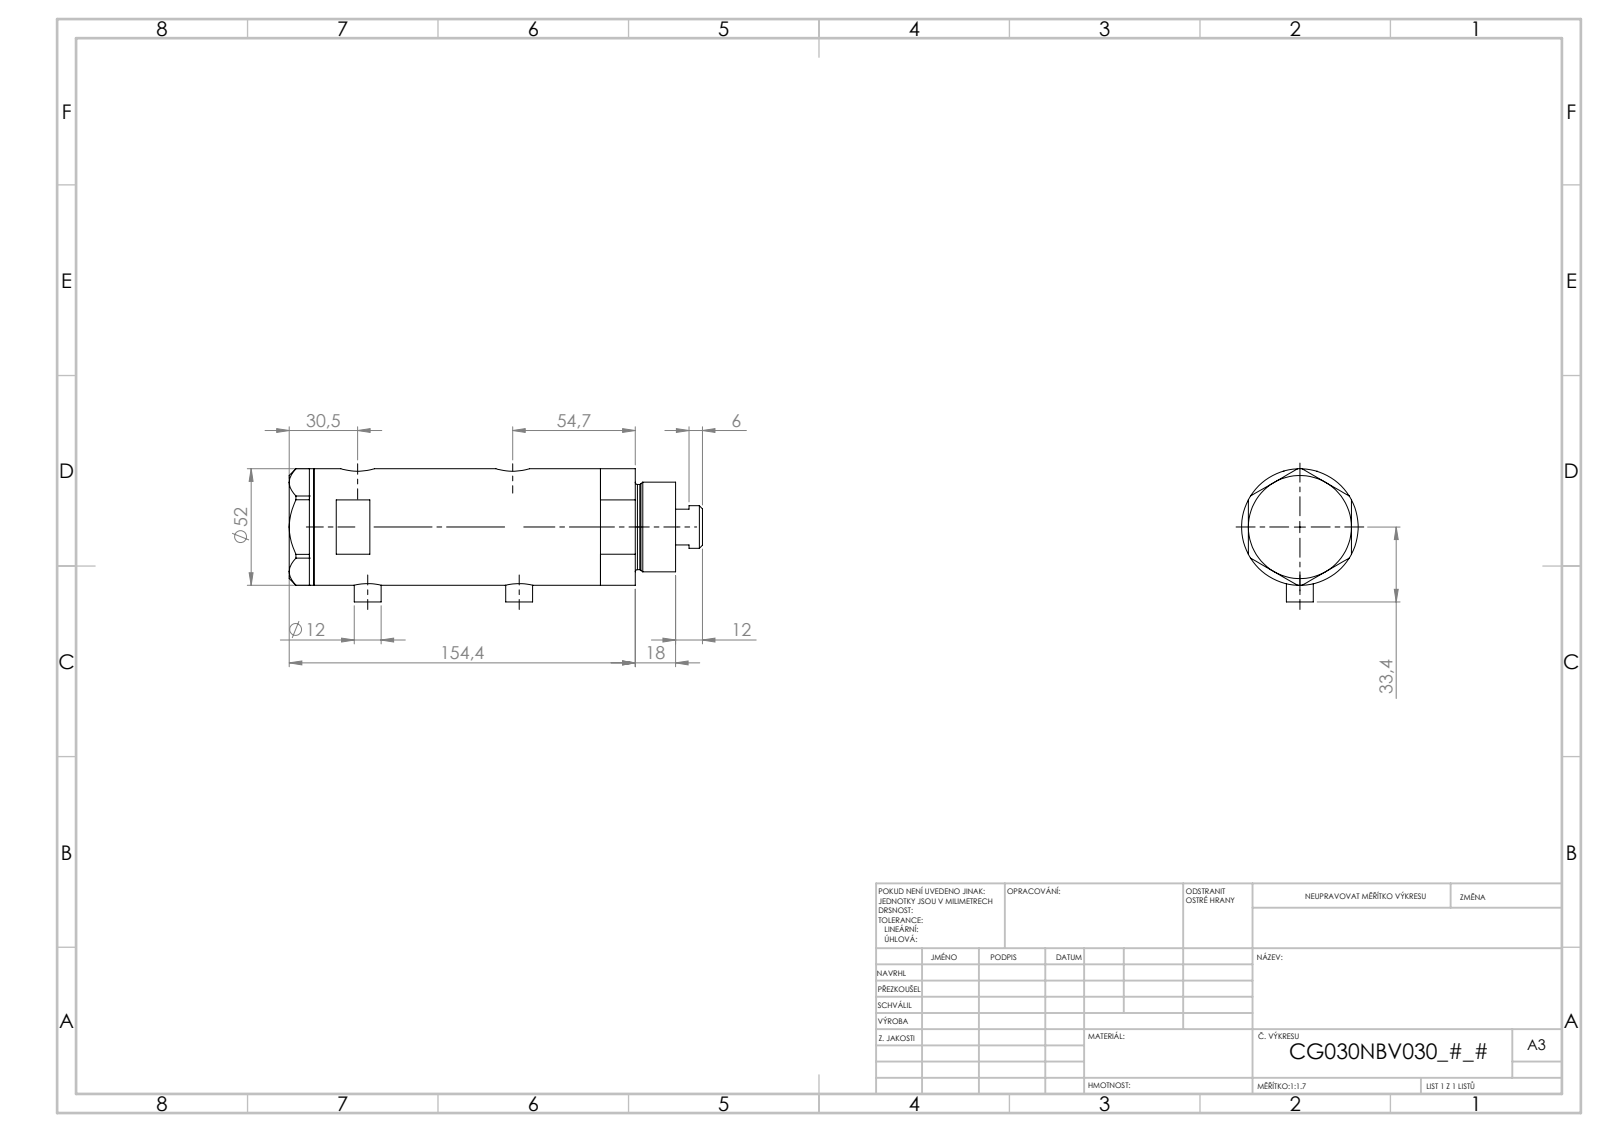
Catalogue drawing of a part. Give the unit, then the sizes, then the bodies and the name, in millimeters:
Units: millimetres
Overall size (bounding box): 184.4 × 59.4 × 52
Round holes (diameter × count): ⌀9.73 ×2, ⌀12.5 ×2, ⌀15 ×2, ⌀6.5 ×1, ⌀20 ×1, ⌀21.5 ×1, ⌀30 ×1, ⌀33 ×1, ⌀44 ×1
Round bosses / shafts (diameter × count): ⌀12 ×2, ⌀52 ×1, ⌀40 ×1, ⌀38 ×1, ⌀19 ×1
Main face-to-face distances: 91.5, 23.8, 67.7, 11, 34.8, 102.5, 46, 138.9, 127.9, 104.1
Hole centre spacings: 2.9, 4.5, 64.7, 67.6, 69.2, 72.1
Volume: 334 920 mm³ · Surface area: 77 135 mm²
Bodies: 4 solids, 134 faces (65 planar, 49 cylindrical, 20 other)
Part name (STEP PRODUCT): V270CG_MIDDLE; V270CG_BACK; V270CG_VC; V270CG_FRONT
STEP written by: SolidWorks 2019 (CONFIG_CONTROL_DESIGN)
